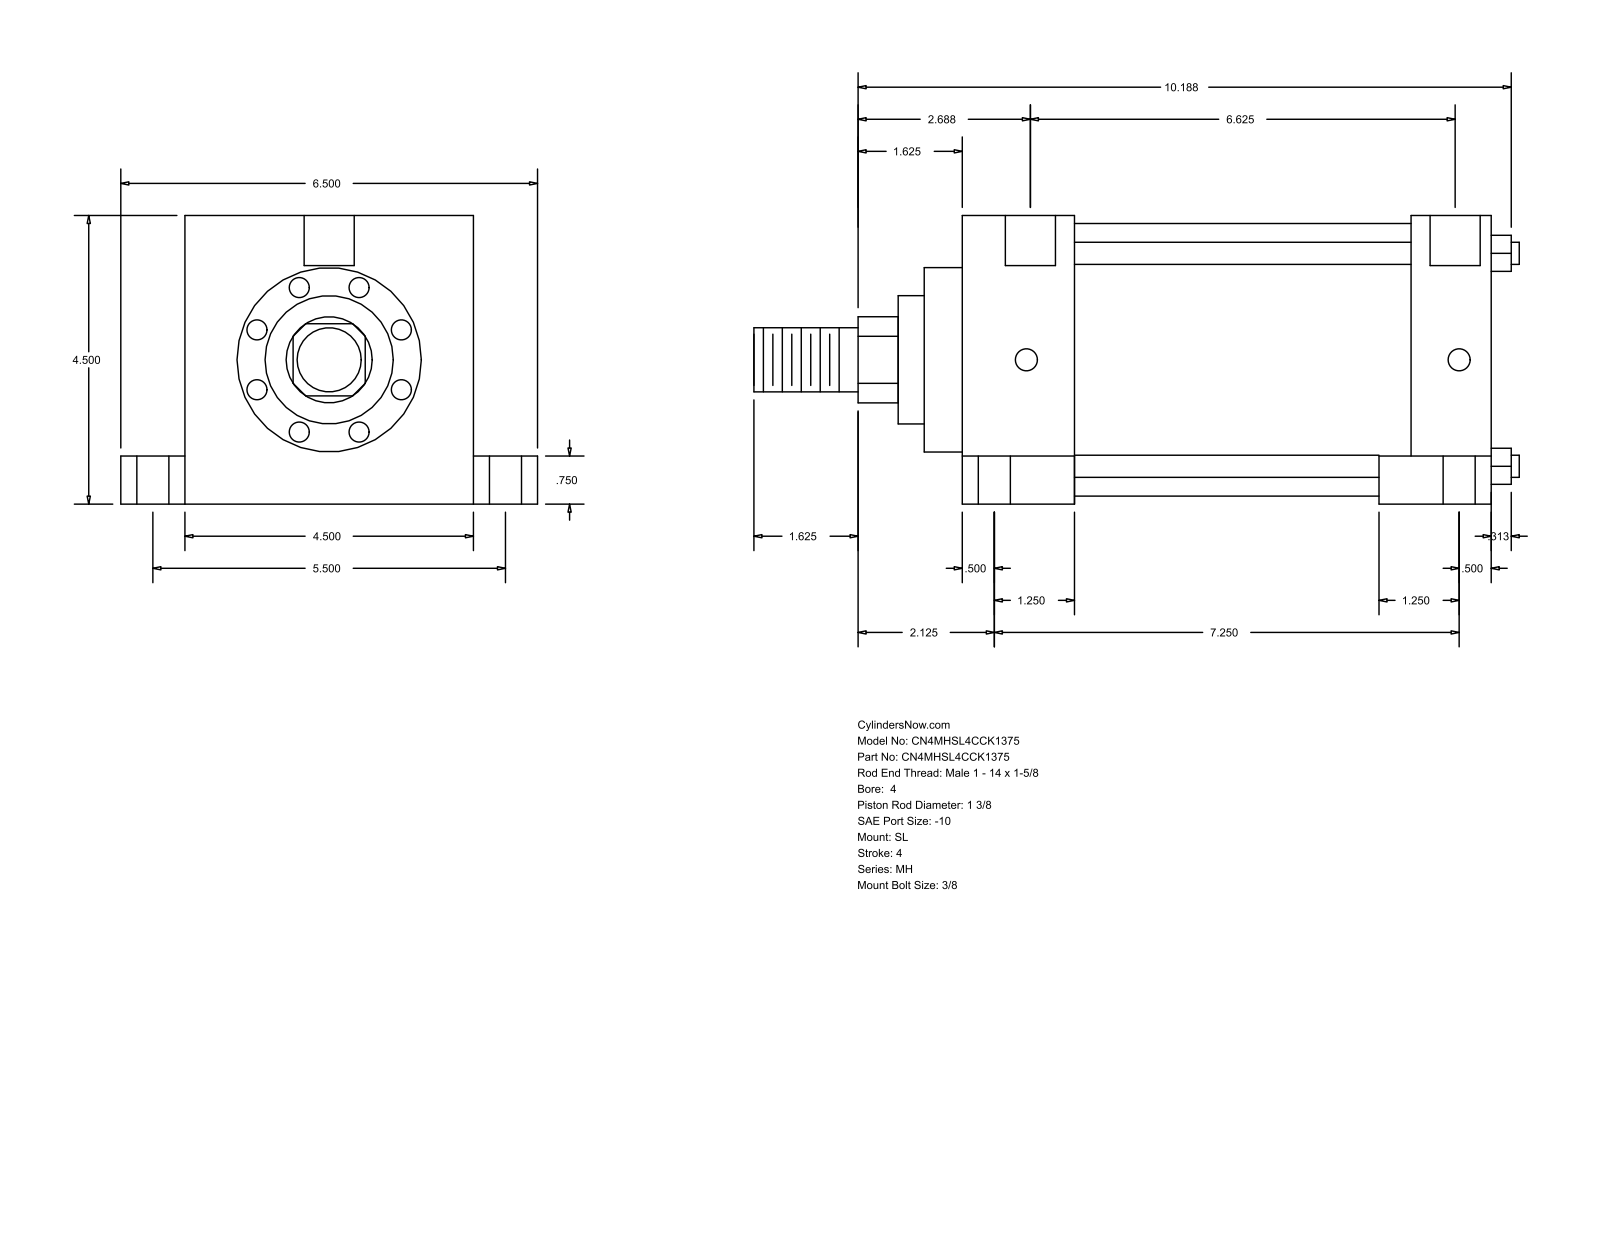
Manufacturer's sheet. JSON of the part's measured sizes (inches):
{"part_name": "MH_SL__0400_1.375", "step_written_by": "GSSL Pune (CONFIG_CONTROL_DESIGN)", "units": "inches", "bodies": {"solids": 0, "faces": 110, "planar": 77, "cylindrical": 33, "other": 0}, "overall_size": [11.937, 6.5, 4.5], "round_holes": [[0.344, 4], [0.5, 4], [0.75, 4], [0.781, 2]], "round_bosses_or_shafts": [[0.345, 4], [4.25, 1], [2.875, 1], [2, 1], [1.375, 1], [1, 1]], "partial_cylinders_radius": [[0.672, 1]], "face_to_face_distances": [4.5, 8.25, 6.5, 1.75, 7, 5.25, 1.25, 1, 5.5, 0.75], "hole_center_spacings": [2.75, 2.751, 2.795, 2.807, 5.5, 6.75, 7.231, 7.25]}
